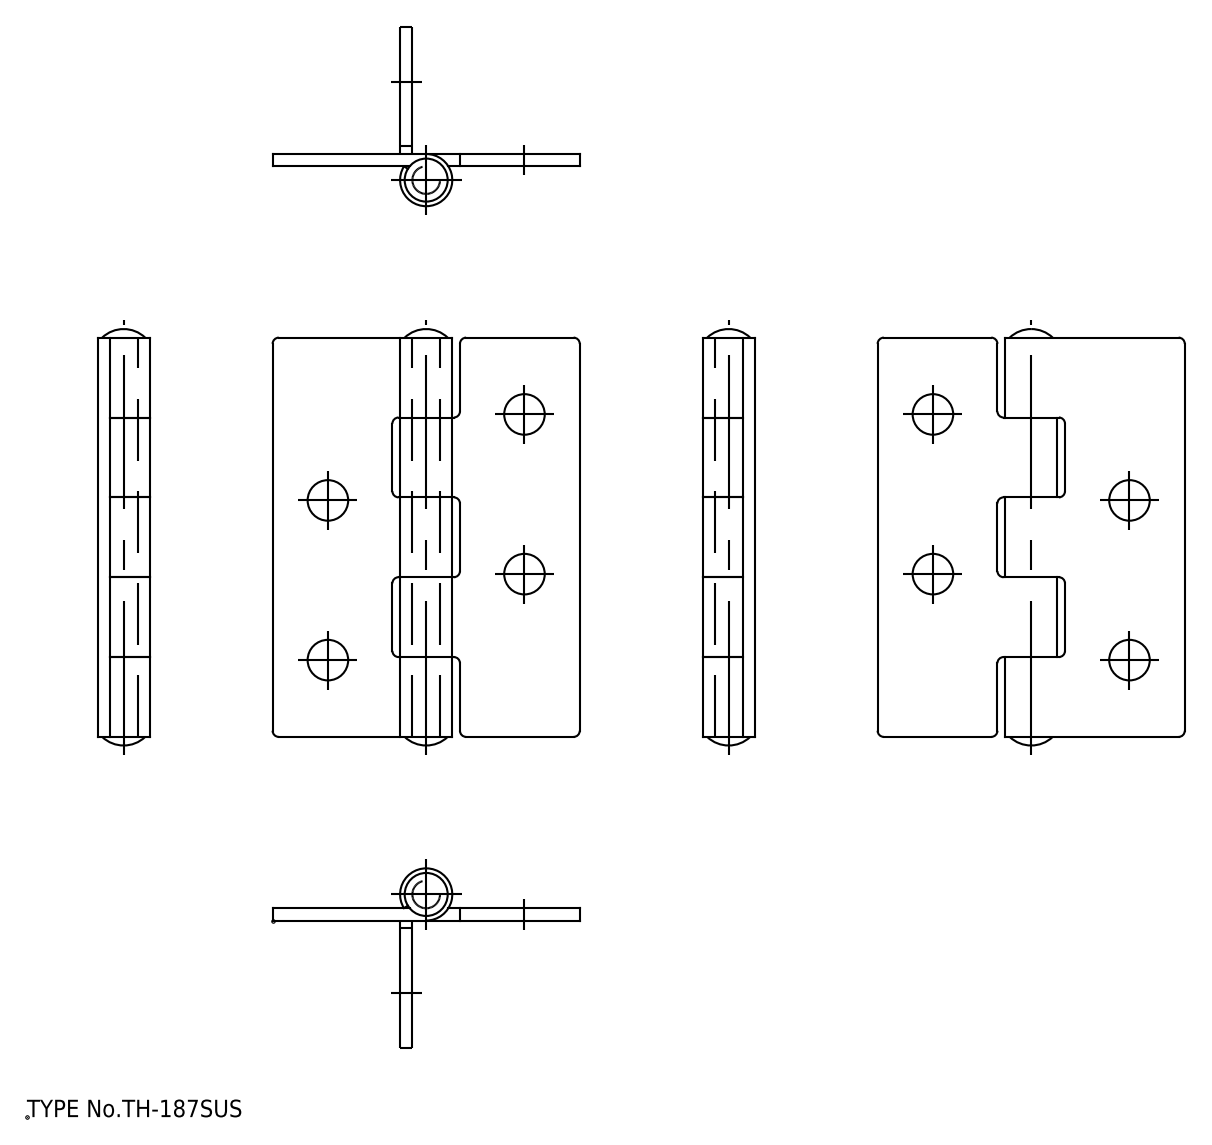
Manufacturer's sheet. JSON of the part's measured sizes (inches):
{"part_name": "TH_187SUS_1; TH_187SUS_2; TH_187SUS_3", "step_written_by": "spGate 19.8.4 (****-****-****-****) (AUTOMOTIVE_DESIGN)", "units": "inches", "bodies": {"solids": 3, "faces": 68, "planar": 30, "cylindrical": 34, "other": 4}, "overall_size": [2.669, 1.969, 0.335], "volume_in3": 0.539, "surface_area_in2": 15.61, "round_holes": [[0.26, 4], [0.177, 1]], "round_bosses_or_shafts": [[0.335, 1]], "partial_cylinders_radius": [[0.039, 14]], "face_to_face_distances": [0.079, 0.512, 1.024, 1.535, 2.047, 2.559, 1.969, 0.768, 1.201, 0.433], "hole_center_spacings": [1.024, 1.375, 1.346, 2.017]}
